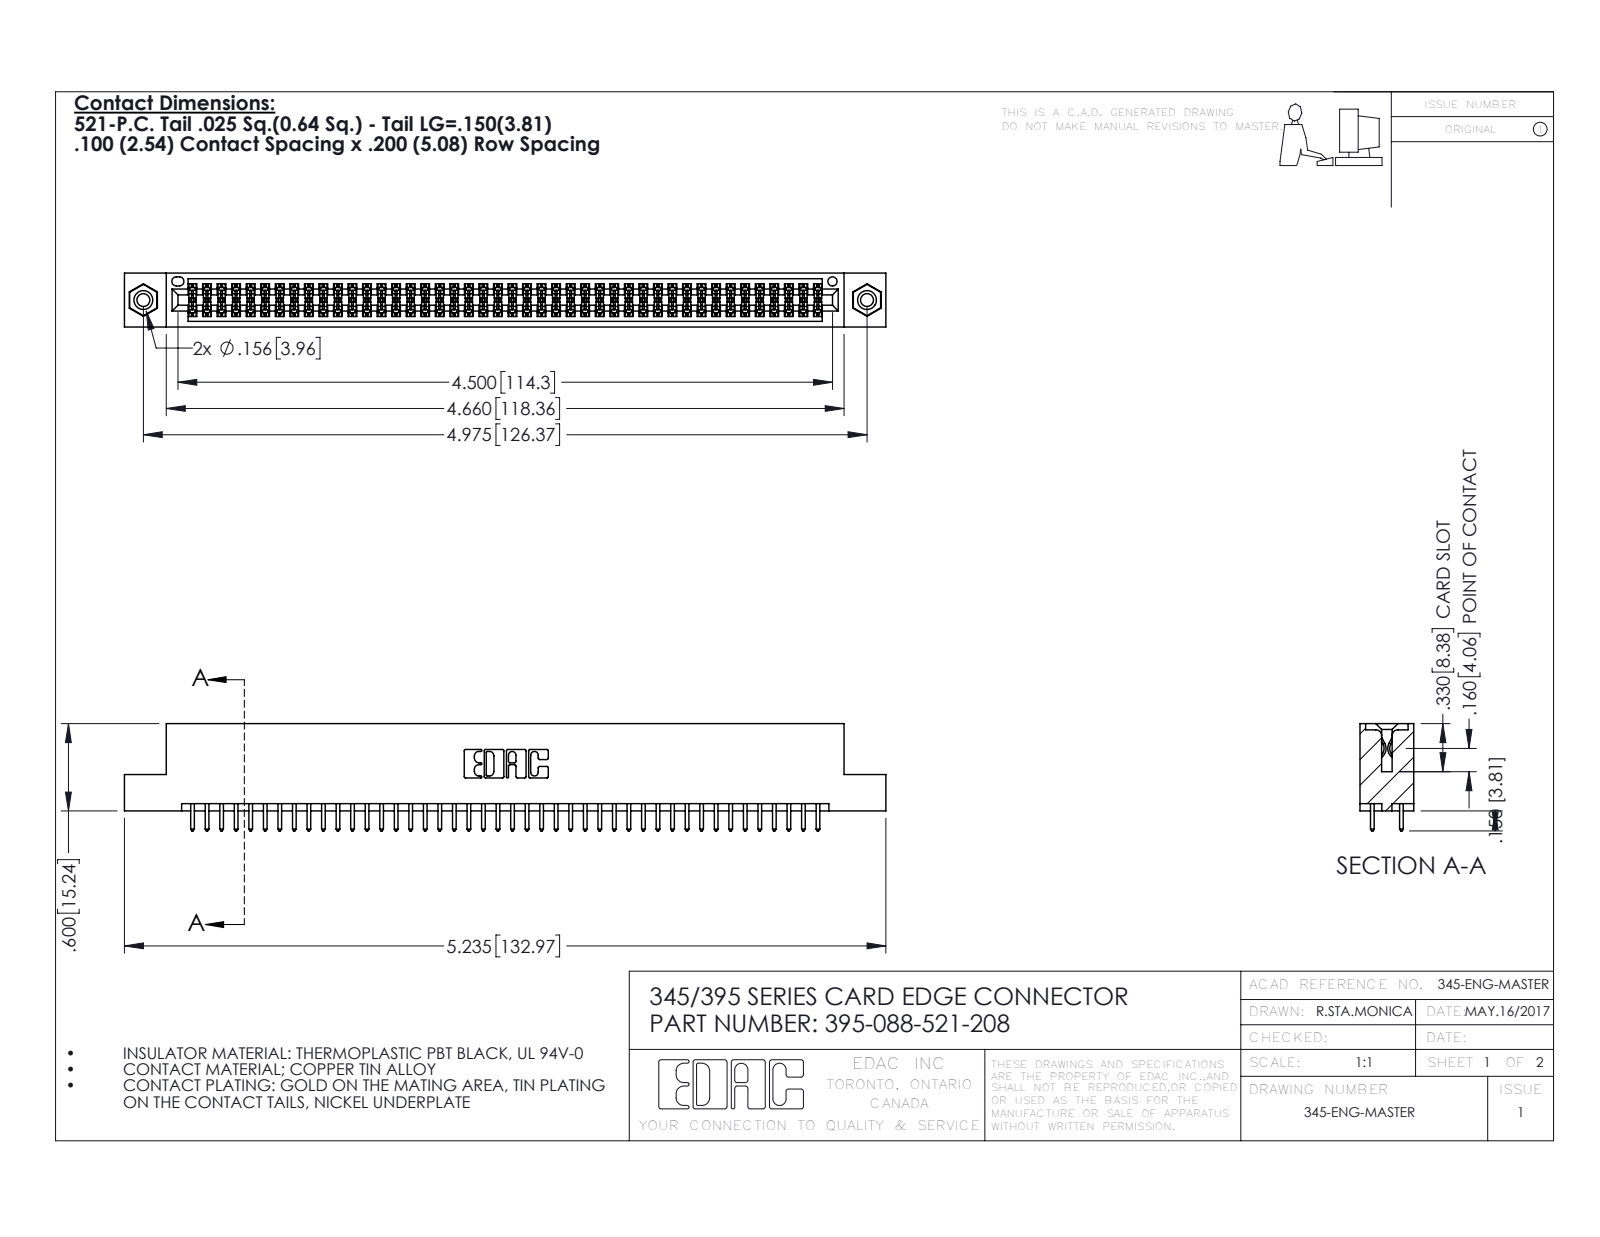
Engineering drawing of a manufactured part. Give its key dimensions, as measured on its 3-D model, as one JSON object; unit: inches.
{"part_name": "345-292-001_345-293-121; 345-250-001_345-250-003-102; 345 Part_Flush Mounting Lugs - 0.156 Dia-TI; 395-088-521-208", "step_written_by": "SolidWorks 2016 (CONFIG_CONTROL_DESIGN)", "units": "inches", "bodies": {"solids": 91, "faces": 4586, "planar": 3016, "cylindrical": 1554, "other": 16}, "overall_size": [5.235, 0.737, 0.37], "volume_in3": 0.787, "surface_area_in2": 29.26, "round_holes": [[0.089, 2], [0.125, 2], [0.156, 2], [0.064, 1]], "round_bosses_or_shafts": [[0.155, 2]], "partial_cylinders_radius": [[0.006, 132], [0.01, 88], [0.01, 22], [0.007, 6], [0.031, 6], [0.026, 3], [0.014, 2], [0.019, 2]], "face_to_face_distances": [0.072, 0.298, 0.2, 0.37, 0.098, 0.272, 0.025, 0.225, 0.175, 0.149], "hole_center_spacings": [0.27, 4.739, 4.975]}
